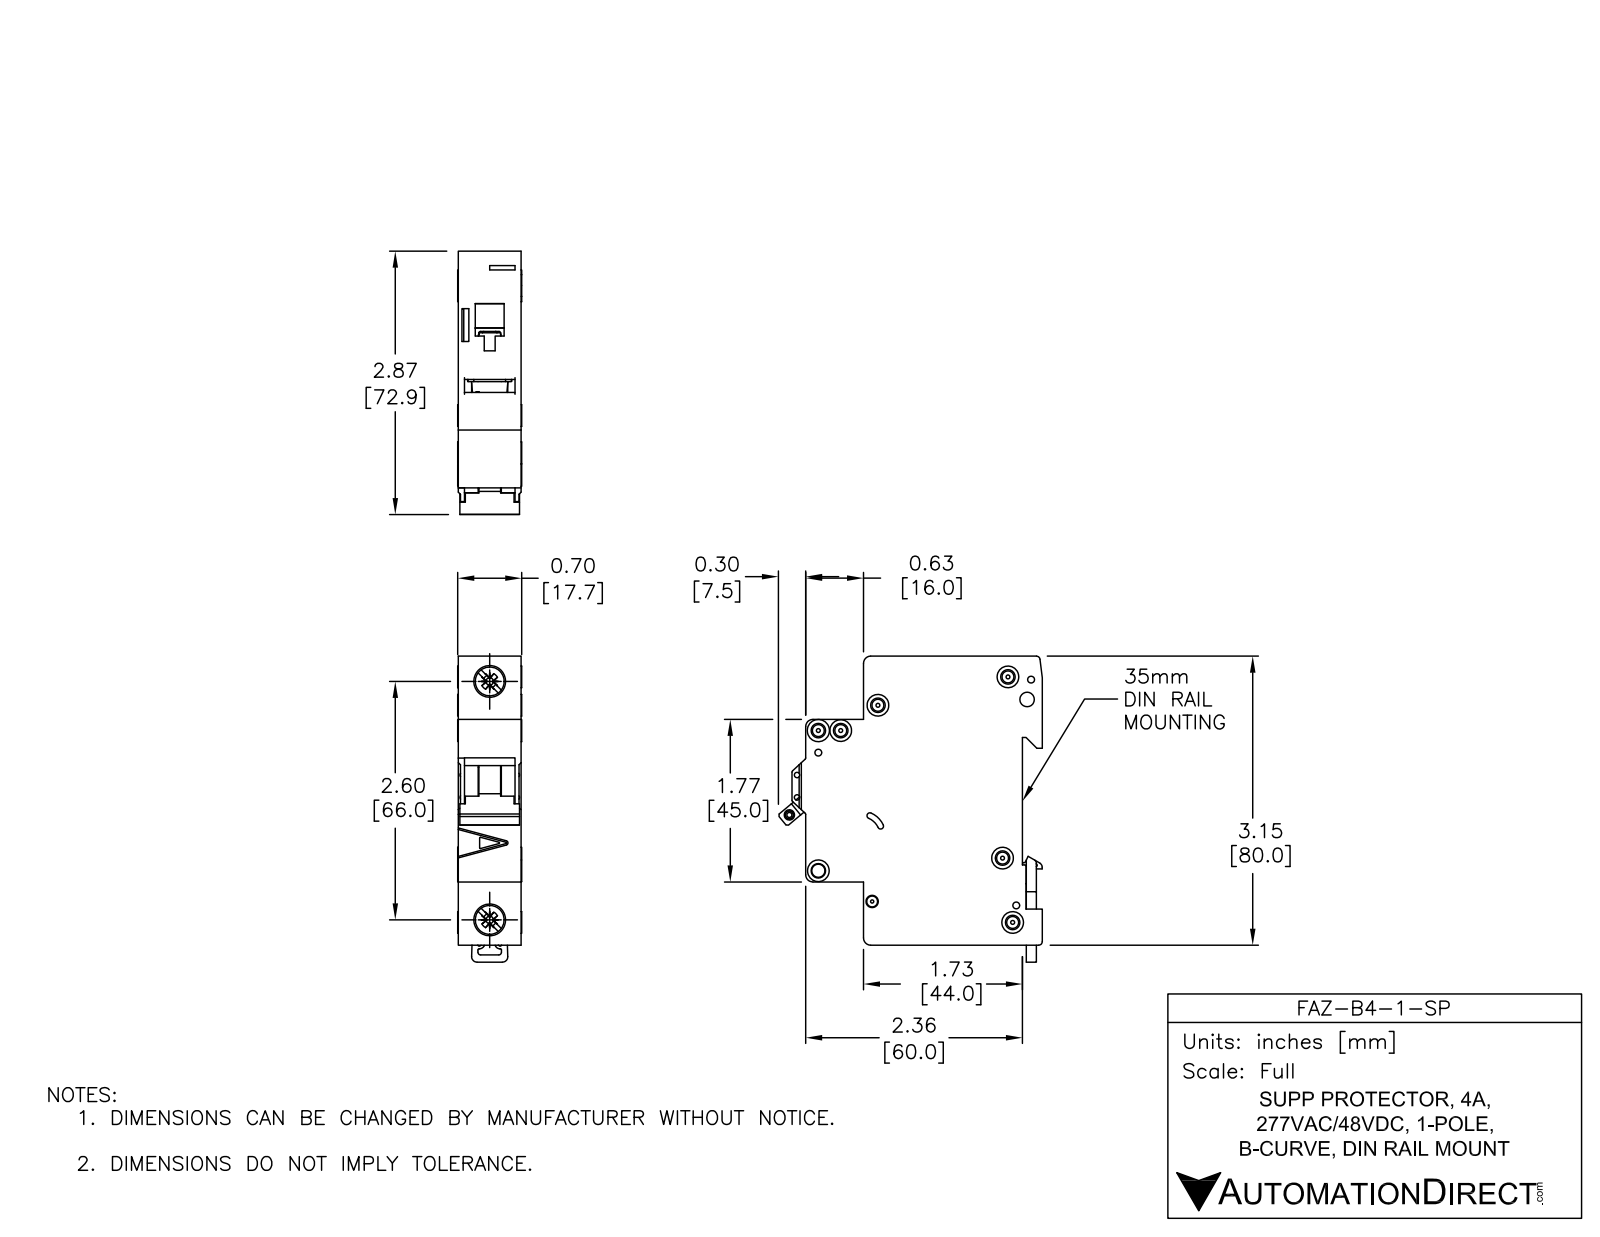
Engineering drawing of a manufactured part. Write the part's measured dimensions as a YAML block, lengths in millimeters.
part_name: "FAZ-B4-1-SP"
step_written_by: "SolidWorks 2014 (AUTOMOTIVE_DESIGN)"
units: millimeters
bodies: {solids: 5, faces: 558, planar: 235, cylindrical: 202, other: 121}
overall_size: [84.78, 73.04, 17.7]
volume: 74935
surface_area: 19545
round_holes:
  - {diameter: 3.6, count: 6}
  - {diameter: 1.9, count: 3}
  - {diameter: 1.09, count: 2}
  - {diameter: 1.5, count: 2}
  - {diameter: 4, count: 2}
  - {diameter: 7.15, count: 2}
  - {diameter: 2.15, count: 1}
  - {diameter: 2.2, count: 1}
  - {diameter: 2.55, count: 1}
  - {diameter: 3.3, count: 1}
  - {diameter: 3.4, count: 1}
round_bosses_or_shafts:
  - {diameter: 6, count: 4}
  - {diameter: 8.2, count: 2}
  - {diameter: 2.5, count: 1}
partial_cylinders:
  - {radius: 0.25, count: 30}
  - {radius: 0.5, count: 13}
  - {radius: 2, count: 8}
  - {radius: 0.2, count: 5}
  - {radius: 1, count: 4}
  - {radius: 0.8, count: 2}
  - {radius: 3, count: 2}
  - {radius: 1.5, count: 1}
face_to_face_distances: [17.5, 79.48, 5.5, 49.5, 44, 65.5, 60, 16, 1.75, 15.75]
hole_center_spacings: [6.2, 13.64, 4.81, 5.19, 5.61, 6.1, 6.44, 8.19]
